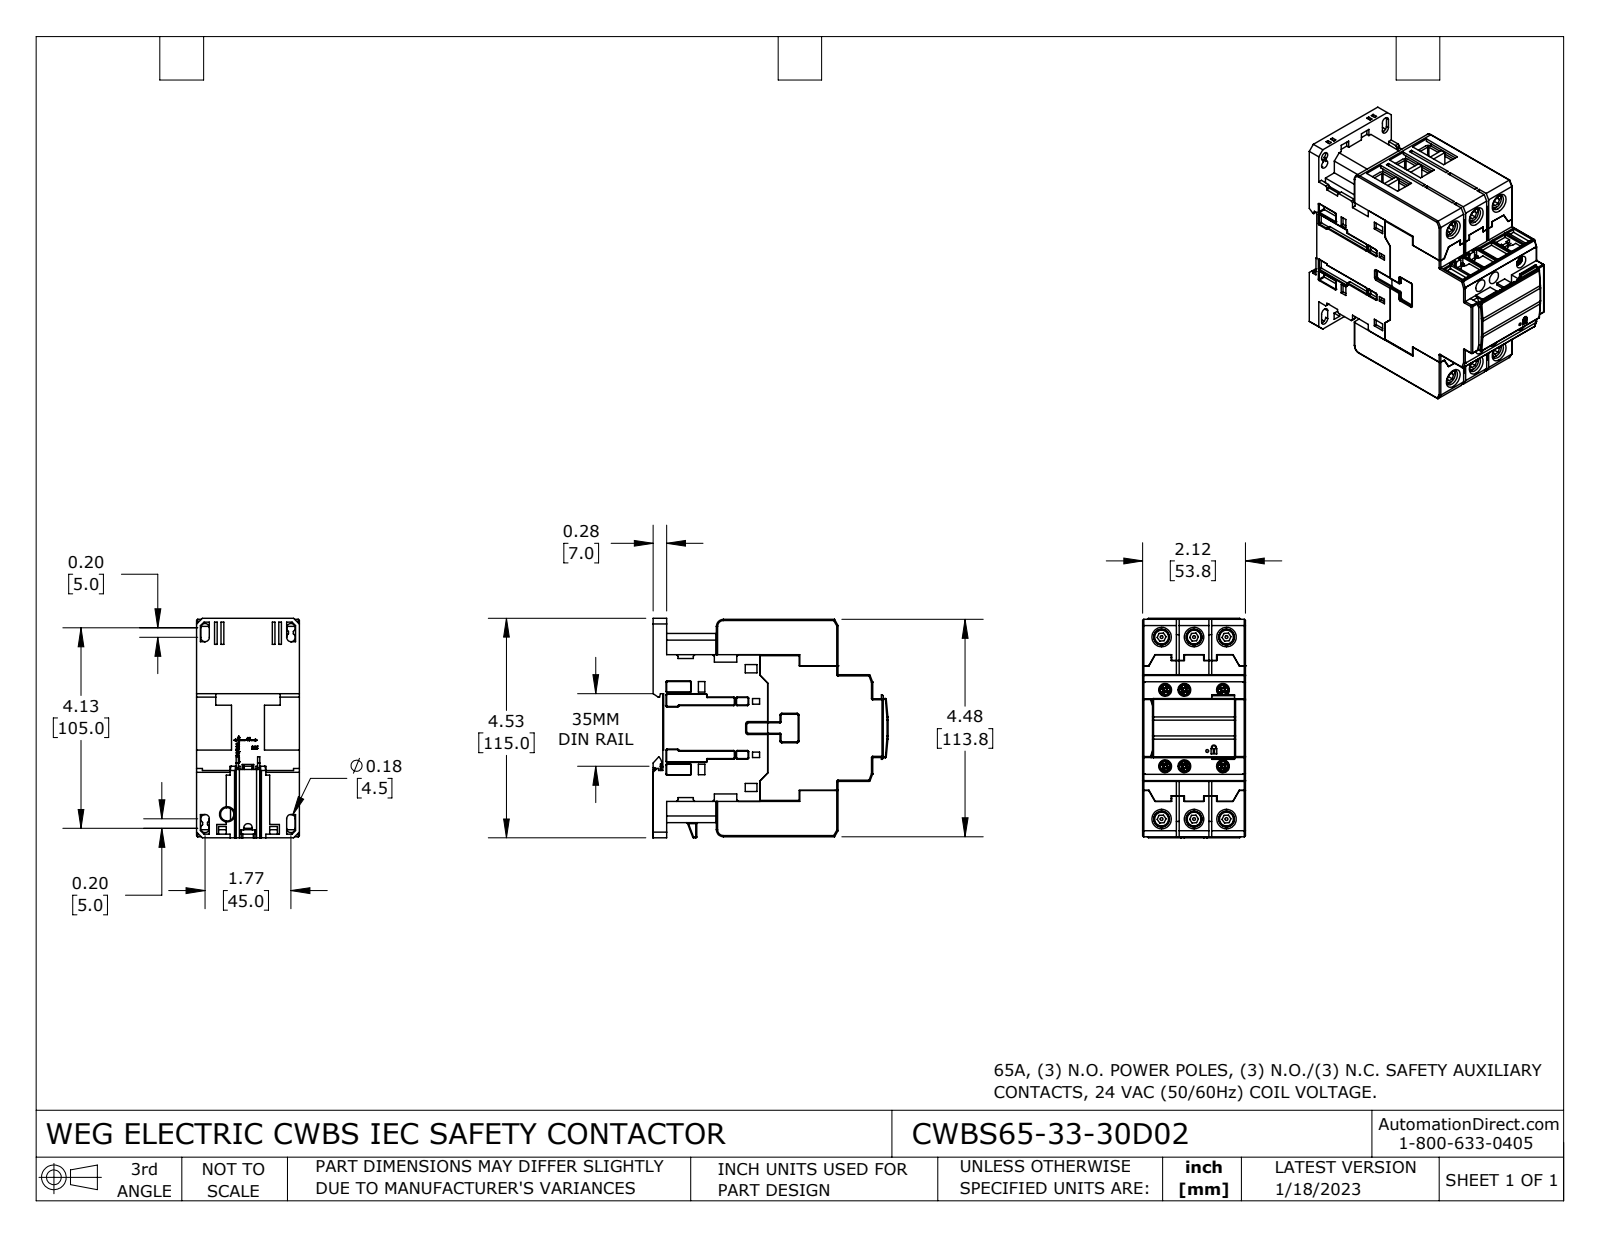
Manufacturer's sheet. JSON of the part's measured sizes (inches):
{"part_name": "CWBS65-33-30D02", "step_written_by": "SolidWorks 2021 (CONFIG_CONTROL_DESIGN)", "units": "inches", "bodies": {"solids": 37, "faces": 2637, "planar": 1669, "cylindrical": 550, "other": 418}, "overall_size": [4.846, 4.528, 2.118], "volume_in3": 33.67, "surface_area_in2": 209.3, "round_holes": [[0.124, 6], [0.197, 6], [0.264, 6], [0.323, 6], [0.177, 4], [0.125, 2], [0.276, 2], [0.059, 1]], "round_bosses_or_shafts": [[0.343, 6], [0.236, 6], [0.135, 6]], "partial_cylinders_radius": [[0.02, 89], [0.012, 69], [0.004, 48], [0.024, 42], [0.079, 18], [0.089, 5], [0.039, 3], [0.059, 3]], "face_to_face_distances": [0.059, 2.118, 0.669, 0.728, 3.024, 3.752, 0.108, 0.217, 3.811, 0.098], "hole_center_spacings": [0.669, 1.091, 1.241, 1.669, 2.665, 2.73, 2.949, 3.811]}
